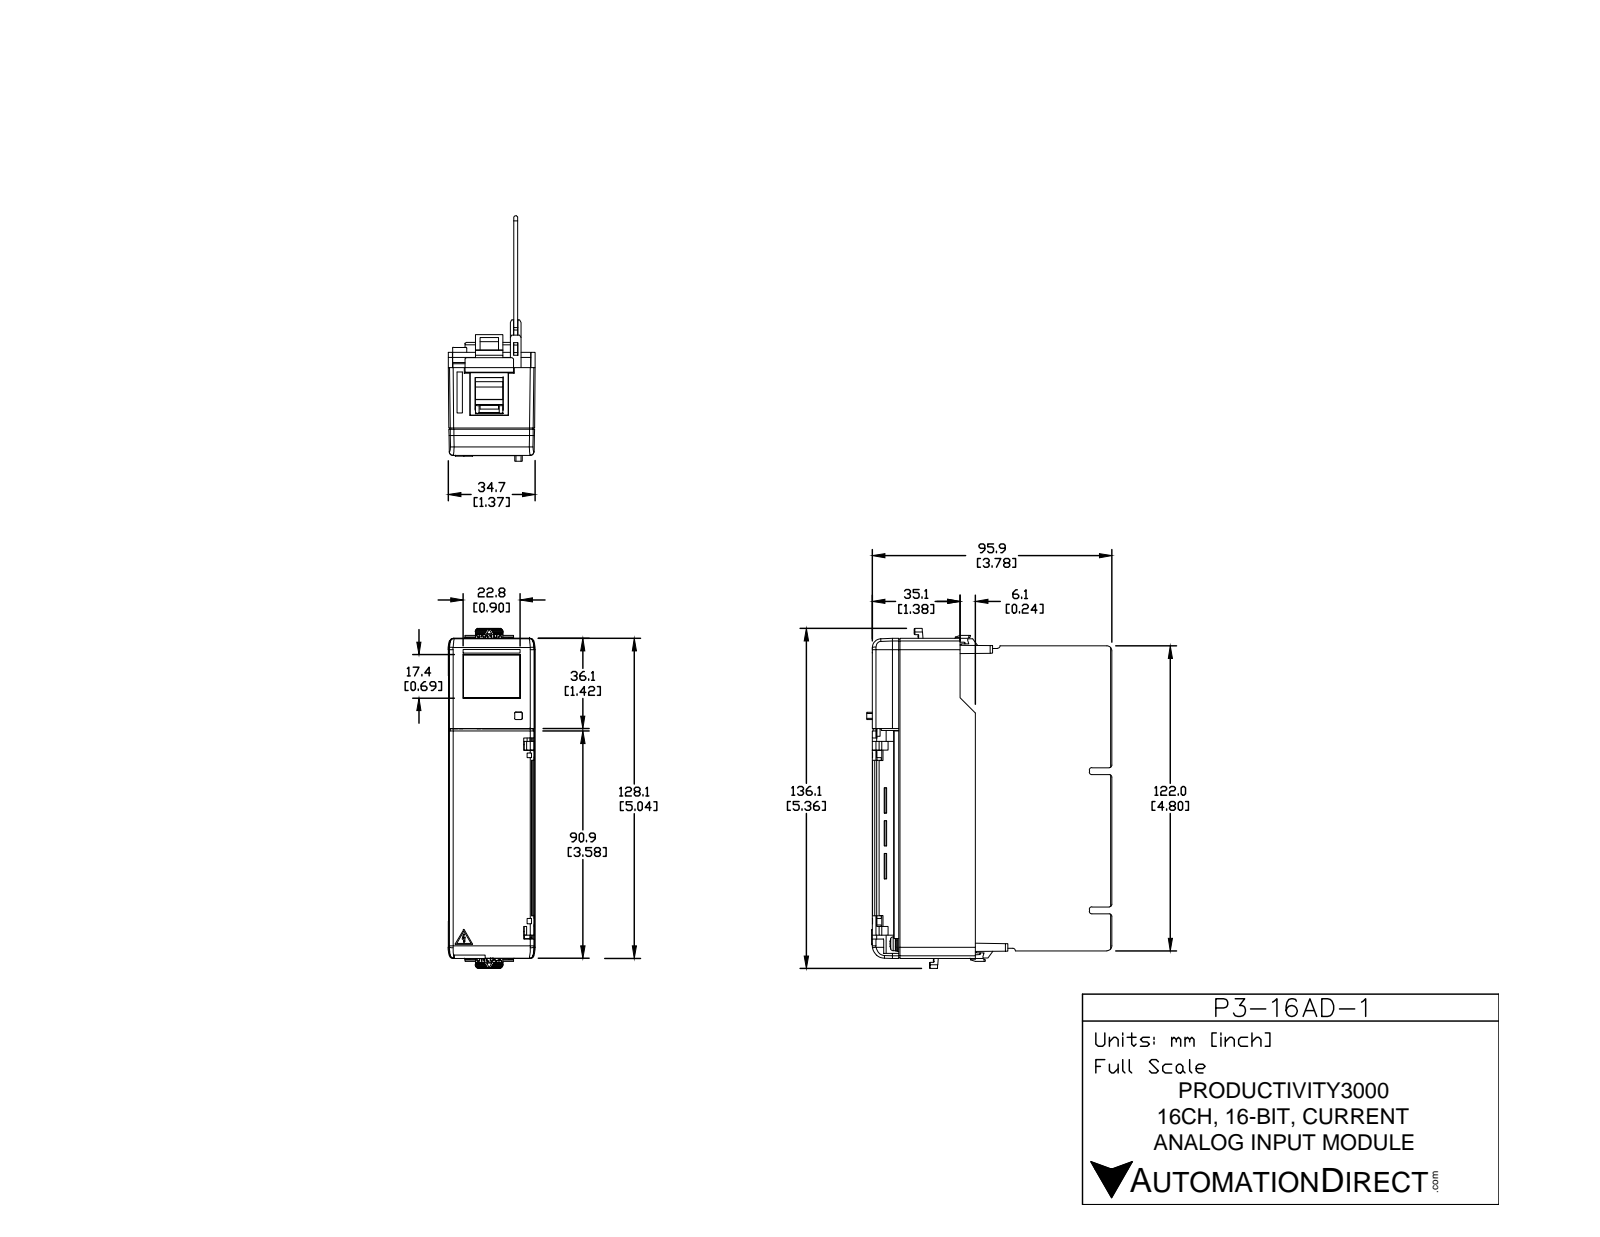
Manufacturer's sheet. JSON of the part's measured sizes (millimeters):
{"part_name": "P3-16AD-1", "step_written_by": "SolidWorks 2009 (CONFIG_CONTROL_DESIGN)", "units": "millimeters", "bodies": {"solids": 1, "faces": 3823, "planar": 2833, "cylindrical": 744, "other": 246}, "overall_size": [136.08, 98.18, 34.8], "volume_mm3": 101360, "surface_area_mm2": 75361, "round_holes": [[3.2, 22], [5, 2], [1.8, 1]], "round_bosses_or_shafts": [[5.5, 22], [3, 22], [2.4, 20], [5.6, 2], [2.2, 2], [2, 2], [1.5, 1]], "partial_cylinders_radius": [[0.5, 95], [1, 33], [0.3, 29], [1.67, 22], [1.5, 13], [2, 6], [0.2, 5], [0.1, 4]], "face_to_face_distances": [1.6, 1.7, 28.23, 26.53, 32.56, 22.2, 2.2, 7.9, 6.8, 5.32], "hole_center_spacings": [8.68, 7.62, 13.84, 15.24, 20.59, 22.86, 27.79, 30.48]}
